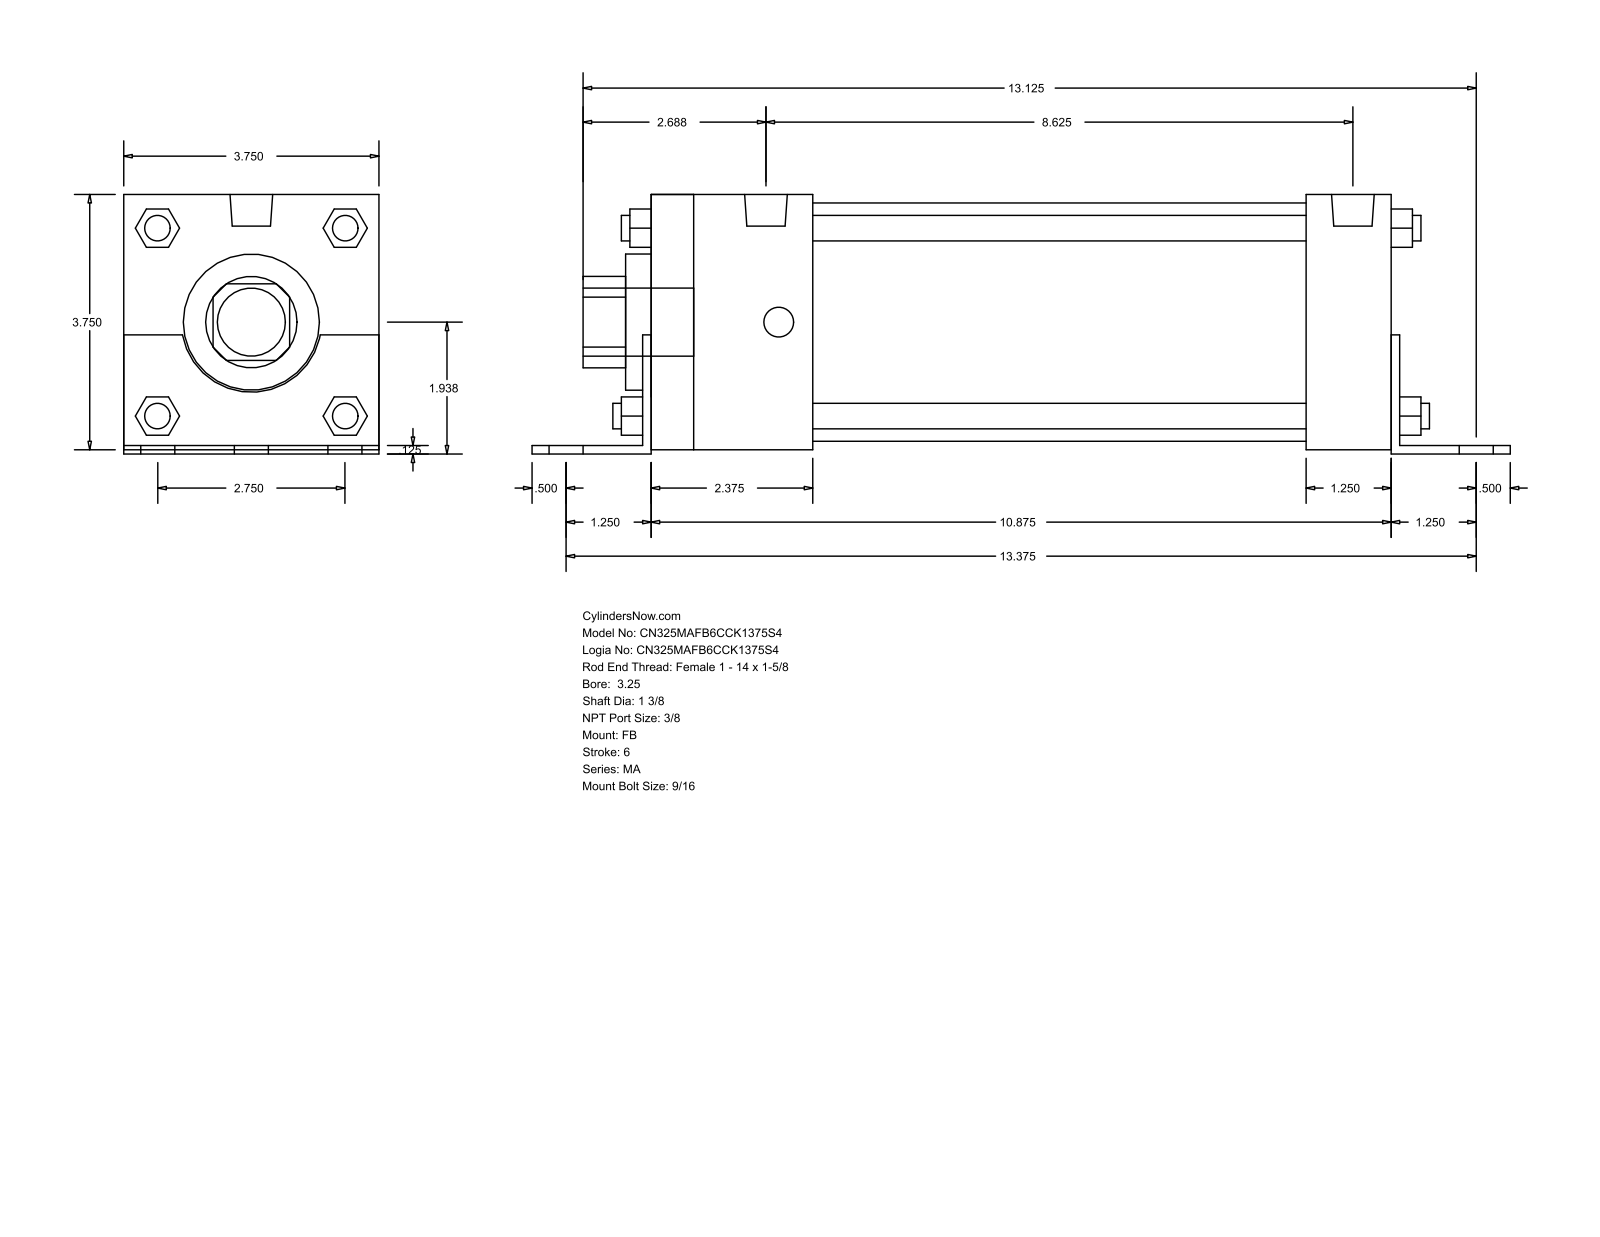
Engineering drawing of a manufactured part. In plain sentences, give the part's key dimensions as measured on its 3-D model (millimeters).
The part is named "MA_FB__0325_1.375". Its 3-D file was written by "GSSL Pune (CONFIG_CONTROL_DESIGN)". It is 0 solids with 140 faces: 105 planar, 35 cylindrical and 0 other. Overall it measures 365.12 by 96.84 by 95.25 millimeters. Round holes: 1 of diameter 34.92, 1 of diameter 50.8, 1 of diameter 88.9. Round bosses or shafts: 6 of diameter 14.29, 4 of diameter 11.11, 4 of diameter 9.53, 2 of diameter 15.93, 1 of diameter 25.4. Partial cylindrical surfaces (rounded edges, fillets, slot ends): 1 of radius 17.06, 1 of radius 26.16. The main face-to-face distances are 95.24, 3.17, 1.59, 96.83, 1.58, 93.66, 3.18, 276.22, 279.4, 60.32.
